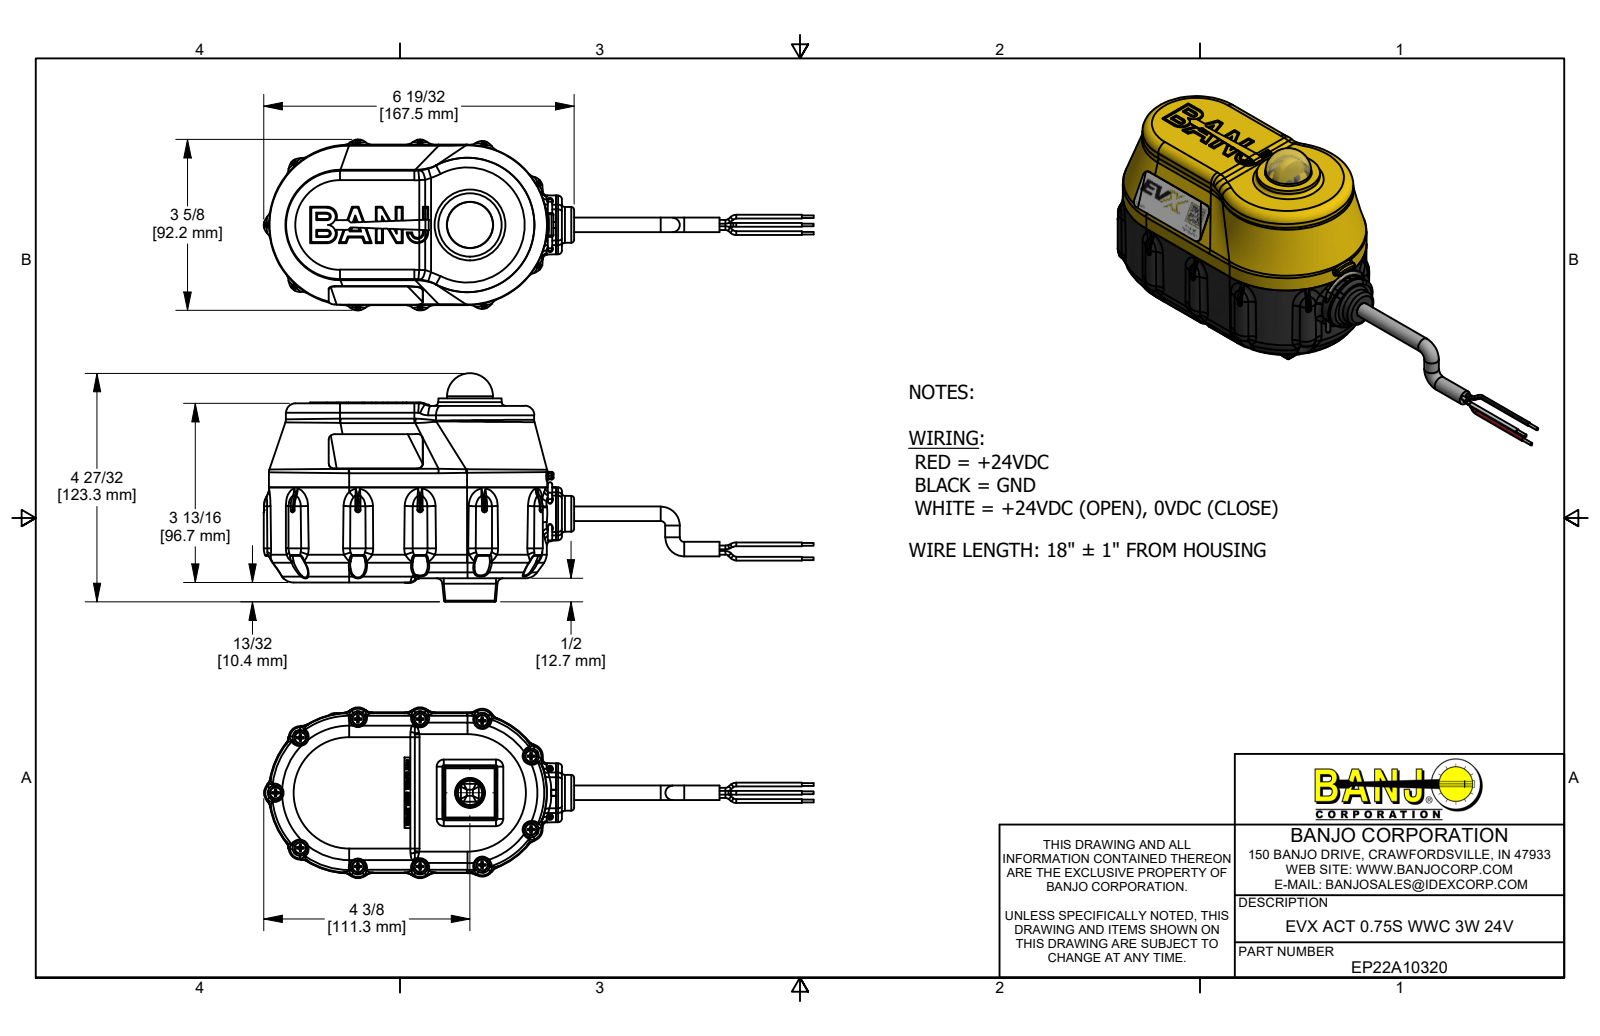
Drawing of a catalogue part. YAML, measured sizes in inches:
part_name: "EP22A10320; B61905PPHS; B632038PM; EP10320 (+8 more)"
step_written_by: "Autodesk Inventor 2019 (AUTOMOTIVE_DESIGN)"
units: inches
bodies: {solids: 72, faces: 9981, planar: 2556, cylindrical: 2922, other: 4503}
overall_size: [6.595, 4.853, 3.63]
volume: 30.67
surface_area: 396.5
round_holes:
  - {diameter: 0.095, count: 11}
  - {diameter: 0.15, count: 11}
  - {diameter: 0.08, count: 7}
  - {diameter: 0.107, count: 4}
  - {diameter: 0.126, count: 4}
  - {diameter: 0.136, count: 4}
  - {diameter: 0.148, count: 4}
  - {diameter: 0.15, count: 4}
  - {diameter: 0.17, count: 4}
  - {diameter: 0.105, count: 2}
  - {diameter: 0.118, count: 2}
  - {diameter: 0.123, count: 2}
round_bosses_or_shafts:
  - {diameter: 0.25, count: 17}
  - {diameter: 0.14, count: 11}
  - {diameter: 0.108, count: 11}
  - {diameter: 0.085, count: 11}
  - {diameter: 0.27, count: 4}
  - {diameter: 0.219, count: 4}
  - {diameter: 0.164, count: 4}
  - {diameter: 0.134, count: 4}
partial_cylinders:
  - {radius: 0.013, count: 180}
  - {radius: 0.04, count: 145}
  - {radius: 0.01, count: 92}
  - {radius: 0.02, count: 71}
  - {radius: 0.005, count: 54}
  - {radius: 0.08, count: 28}
  - {radius: 0.03, count: 26}
  - {radius: 0.1, count: 22}
face_to_face_distances: [0.1, 2.565, 0.211, 0.06, 0.151, 1.685, 1.836, 1.896, 2.465, 0.78]
hole_center_spacings: [1.283, 1.513, 2.69, 2.849, 3.789, 0.487, 0.668, 1.226]
